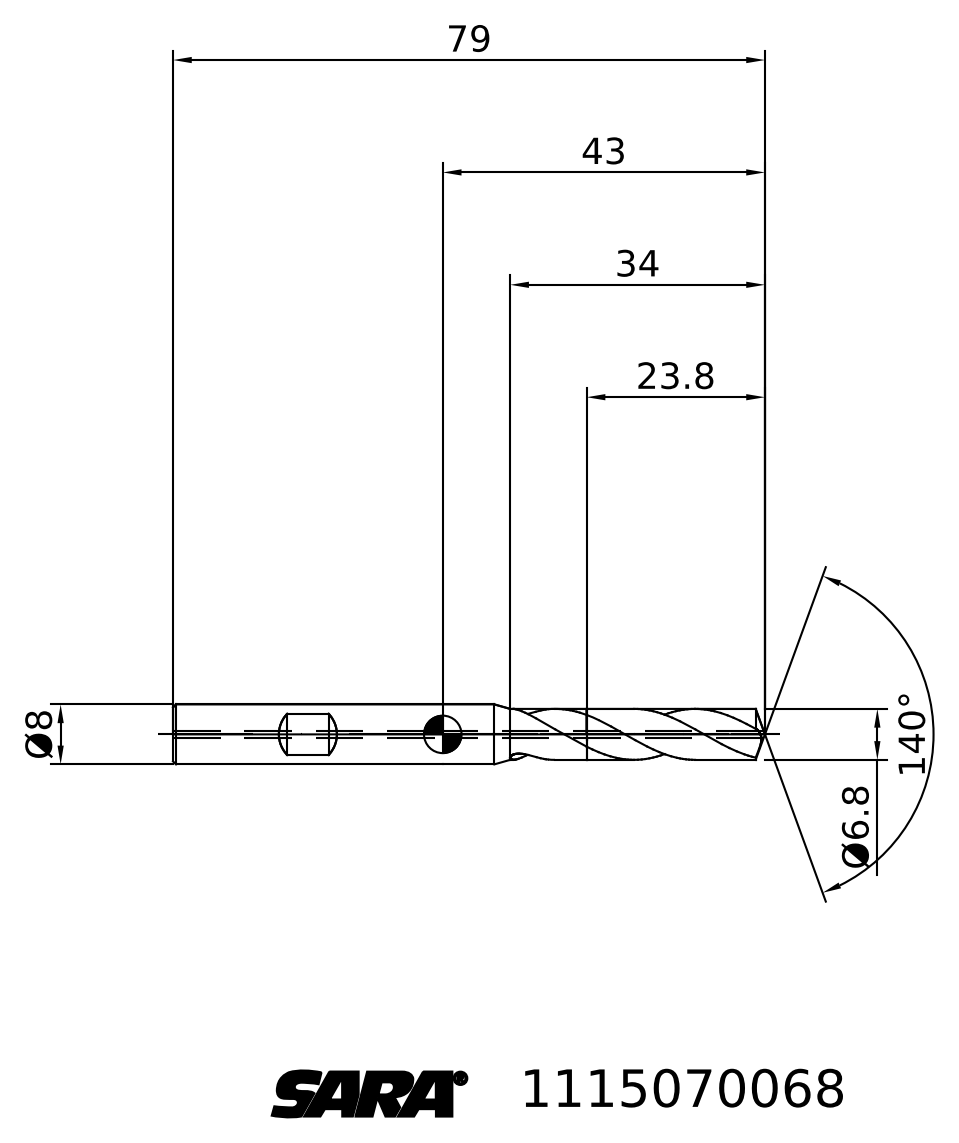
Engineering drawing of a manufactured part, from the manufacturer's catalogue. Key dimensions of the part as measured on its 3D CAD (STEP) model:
STEP written by: TDM (AUTOMOTIVE_DESIGN)
Units: millimetres
Bodies: 2 solids, 30 faces (6 planar, 0 cylindrical, 24 other)
Overall size (bounding box): 79 × 8 × 8
Volume: 3 035 mm³ · Surface area: 2 012 mm²
Main face-to-face distances: 55.2
